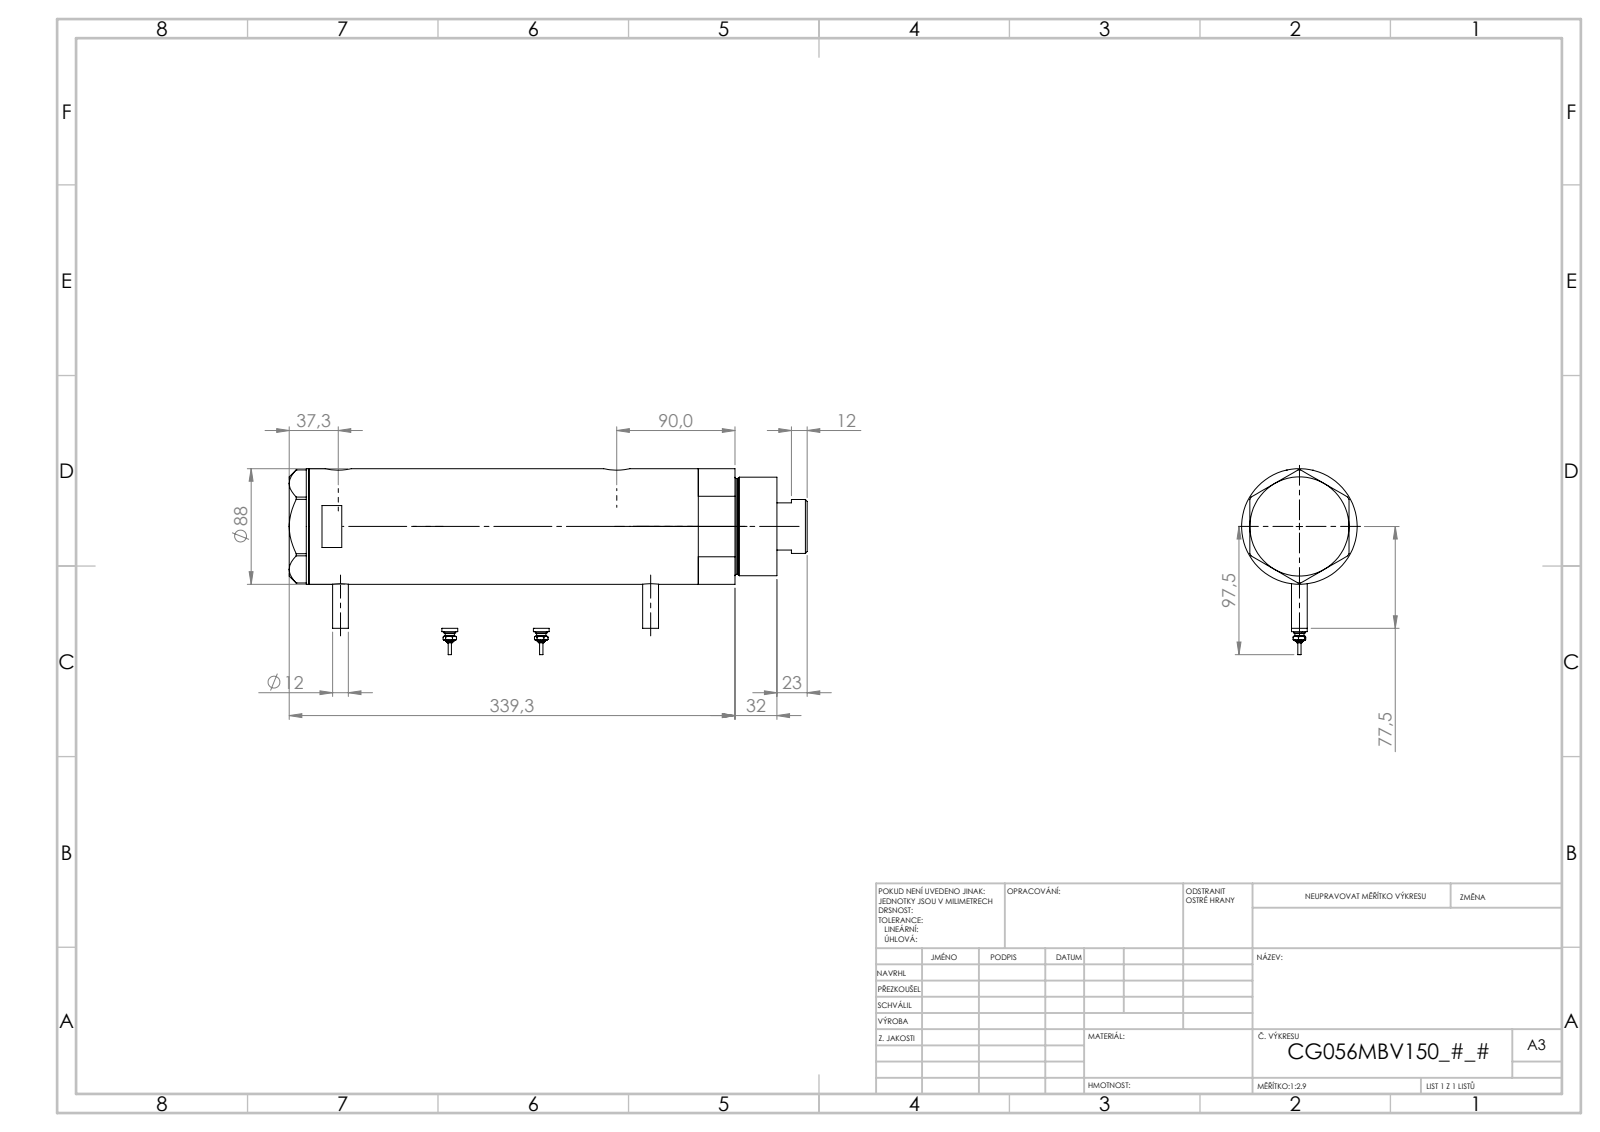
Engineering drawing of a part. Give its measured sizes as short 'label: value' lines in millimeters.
name: V270CG_MIDDLE; V270CG_BACK; V270CG_FRONT; V270CG_VC (+1 more)
written by: SolidWorks 2019 (CONFIG_CONTROL_DESIGN)
unit: mm
bodies: 6 solids, 213 faces (80 planar, 69 cylindrical, 64 other)
size: 394.3 × 141.5 × 88
volume: 2 042 000 mm³; area: 283 023 mm²
holes: 2× ⌀12.5, 2× ⌀13.16, 2× ⌀20, 1× ⌀14.5, 1× ⌀42, 1× ⌀43.5, 1× ⌀56, 1× ⌀60, 1× ⌀80
bosses: 4× ⌀12, 2× ⌀9, 2× ⌀7, 2× ⌀4.5, 2× ⌀2.5, 1× ⌀88, 1× ⌀75, 1× ⌀73
face distances: 234.4, 26, 208.4, 15, 41, 249.4, 356.3, 371.3, 330.3, 121.9
hole spacings: 1.7, 25.8, 210.3, 212, 236.1, 237.8
